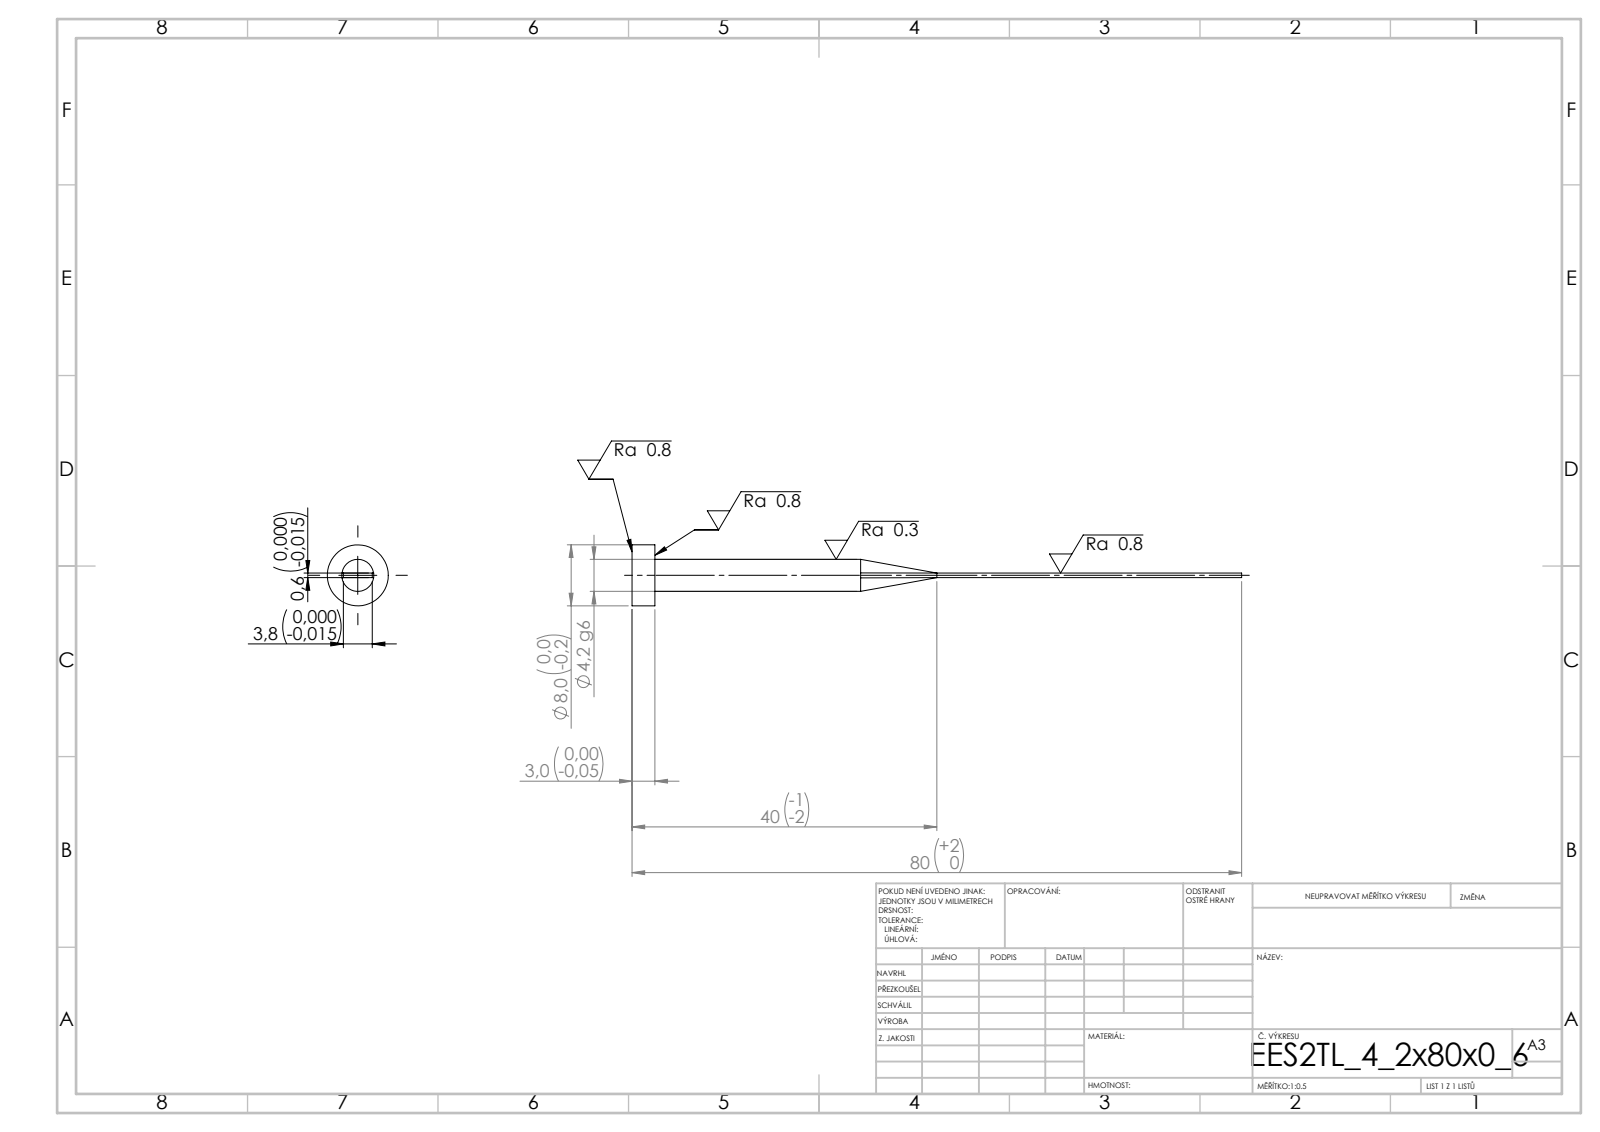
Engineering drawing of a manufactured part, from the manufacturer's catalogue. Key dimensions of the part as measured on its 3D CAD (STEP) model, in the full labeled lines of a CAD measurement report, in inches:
STEP written by: SolidWorks 2019 (CONFIG_CONTROL_DESIGN)
Units: inches
Bodies: 1 solid, 15 faces (7 planar, 4 cylindrical, 4 other)
Overall size (bounding box): 3.15 × 0.315 × 0.315
Volume: 0.042 in³ · Surface area: 1.52 in²
Round bosses / shafts (diameter × count): ⌀0.315 ×1, ⌀0.165 ×1
Main face-to-face distances: 0.024, 0.118, 0.15, 3.15, 3.031
